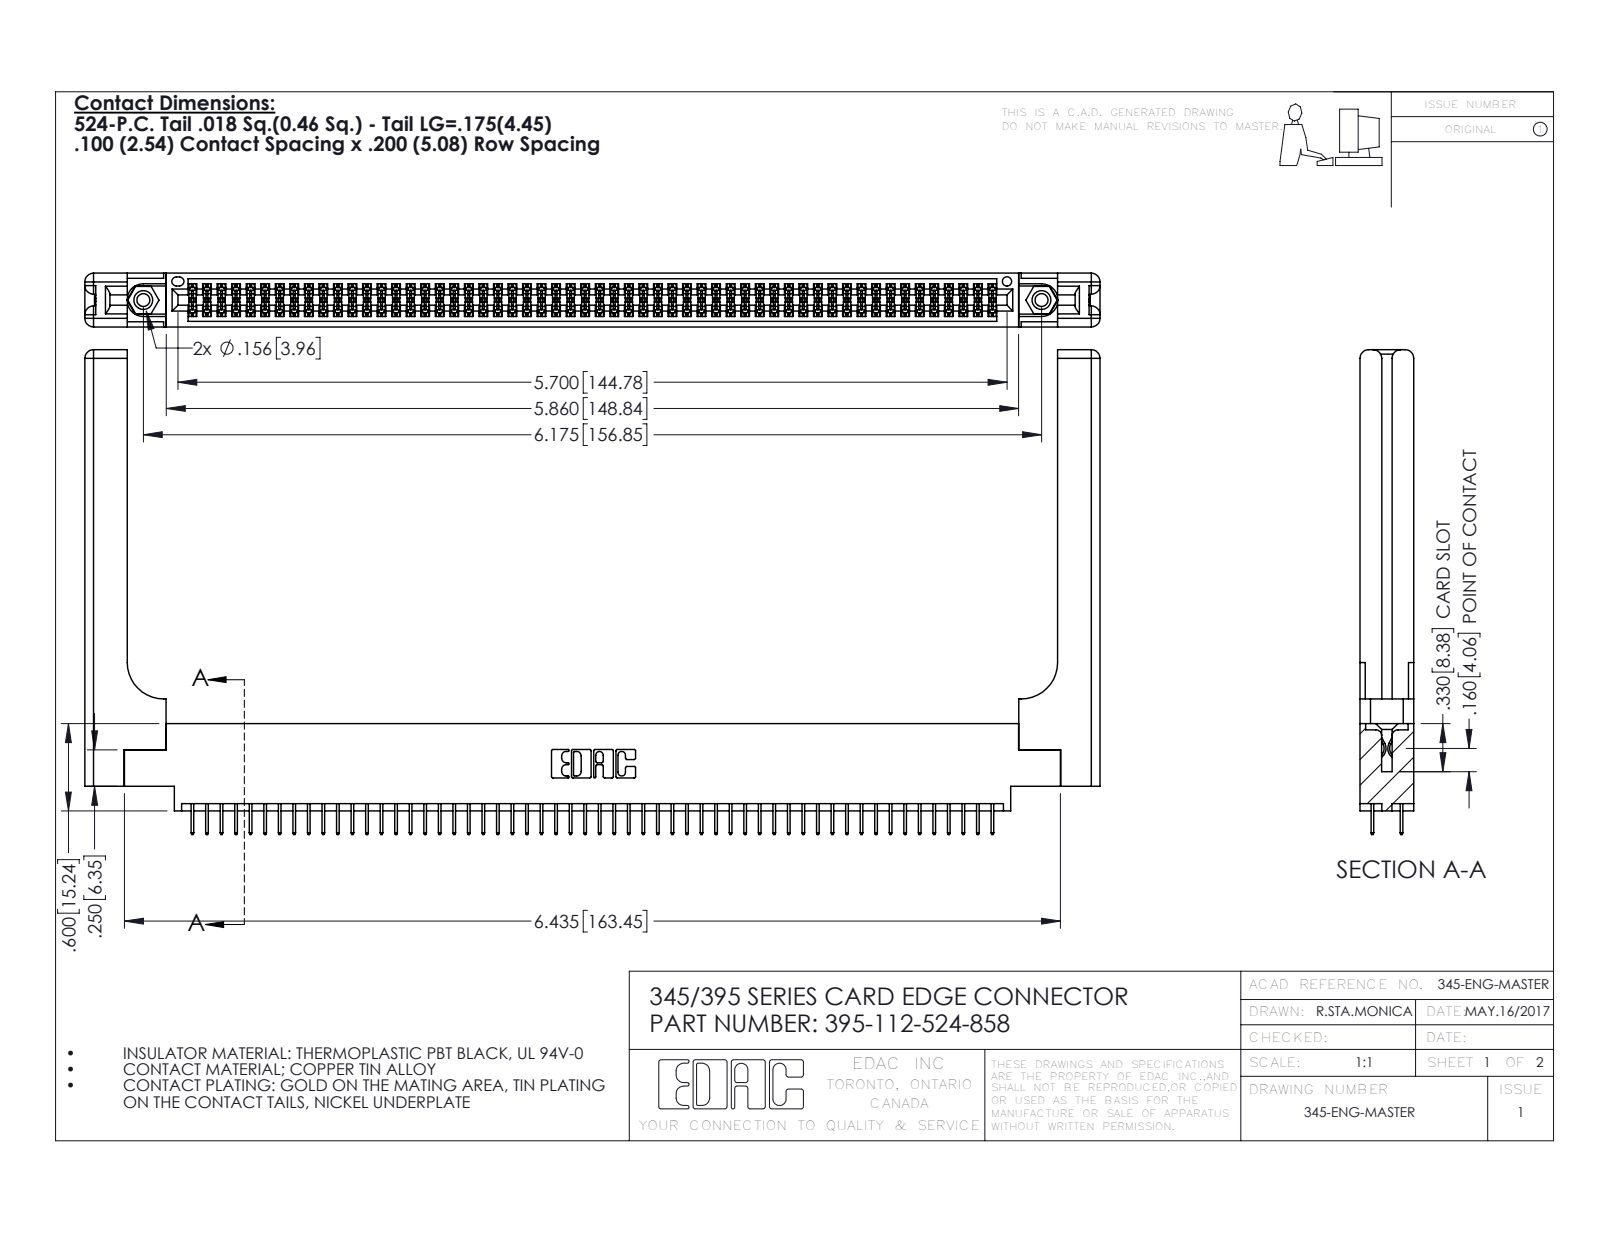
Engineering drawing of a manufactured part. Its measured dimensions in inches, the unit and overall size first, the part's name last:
Units: inches
Overall size (bounding box): 6.979 × 3.332 × 0.37
Round holes (diameter × count): ⌀0.089 ×2, ⌀0.125 ×2, ⌀0.156 ×2, ⌀0.064 ×1
Round bosses / shafts (diameter × count): ⌀0.155 ×2
Partial cylindrical surfaces — rounded edges, fillets, slot ends (radius × count): R0.006 ×168, R0.01 ×22, R0.06 ×16, R0.007 ×6, R0.031 ×6, R0.026 ×3, R0.014 ×2, R0.019 ×2
Main face-to-face distances: 0.072, 0.37, 0.298, 0.2, 0.098, 0.272, 0.025, 0.225, 0.175, 0.148
Hole centre spacings: 0.27, 5.939, 6.175
Volume: 1.559 in³ · Surface area: 46.89 in²
Bodies: 117 solids, 6434 faces (4600 planar, 1774 cylindrical, 60 other)
Part name (STEP PRODUCT): 345-292-001_345-293-124; 345-220-058_345-220-058; 395-112-524-858; 345-250-001_345-250-001-102 (+1 more)
STEP written by: SolidWorks 2016 (CONFIG_CONTROL_DESIGN)
